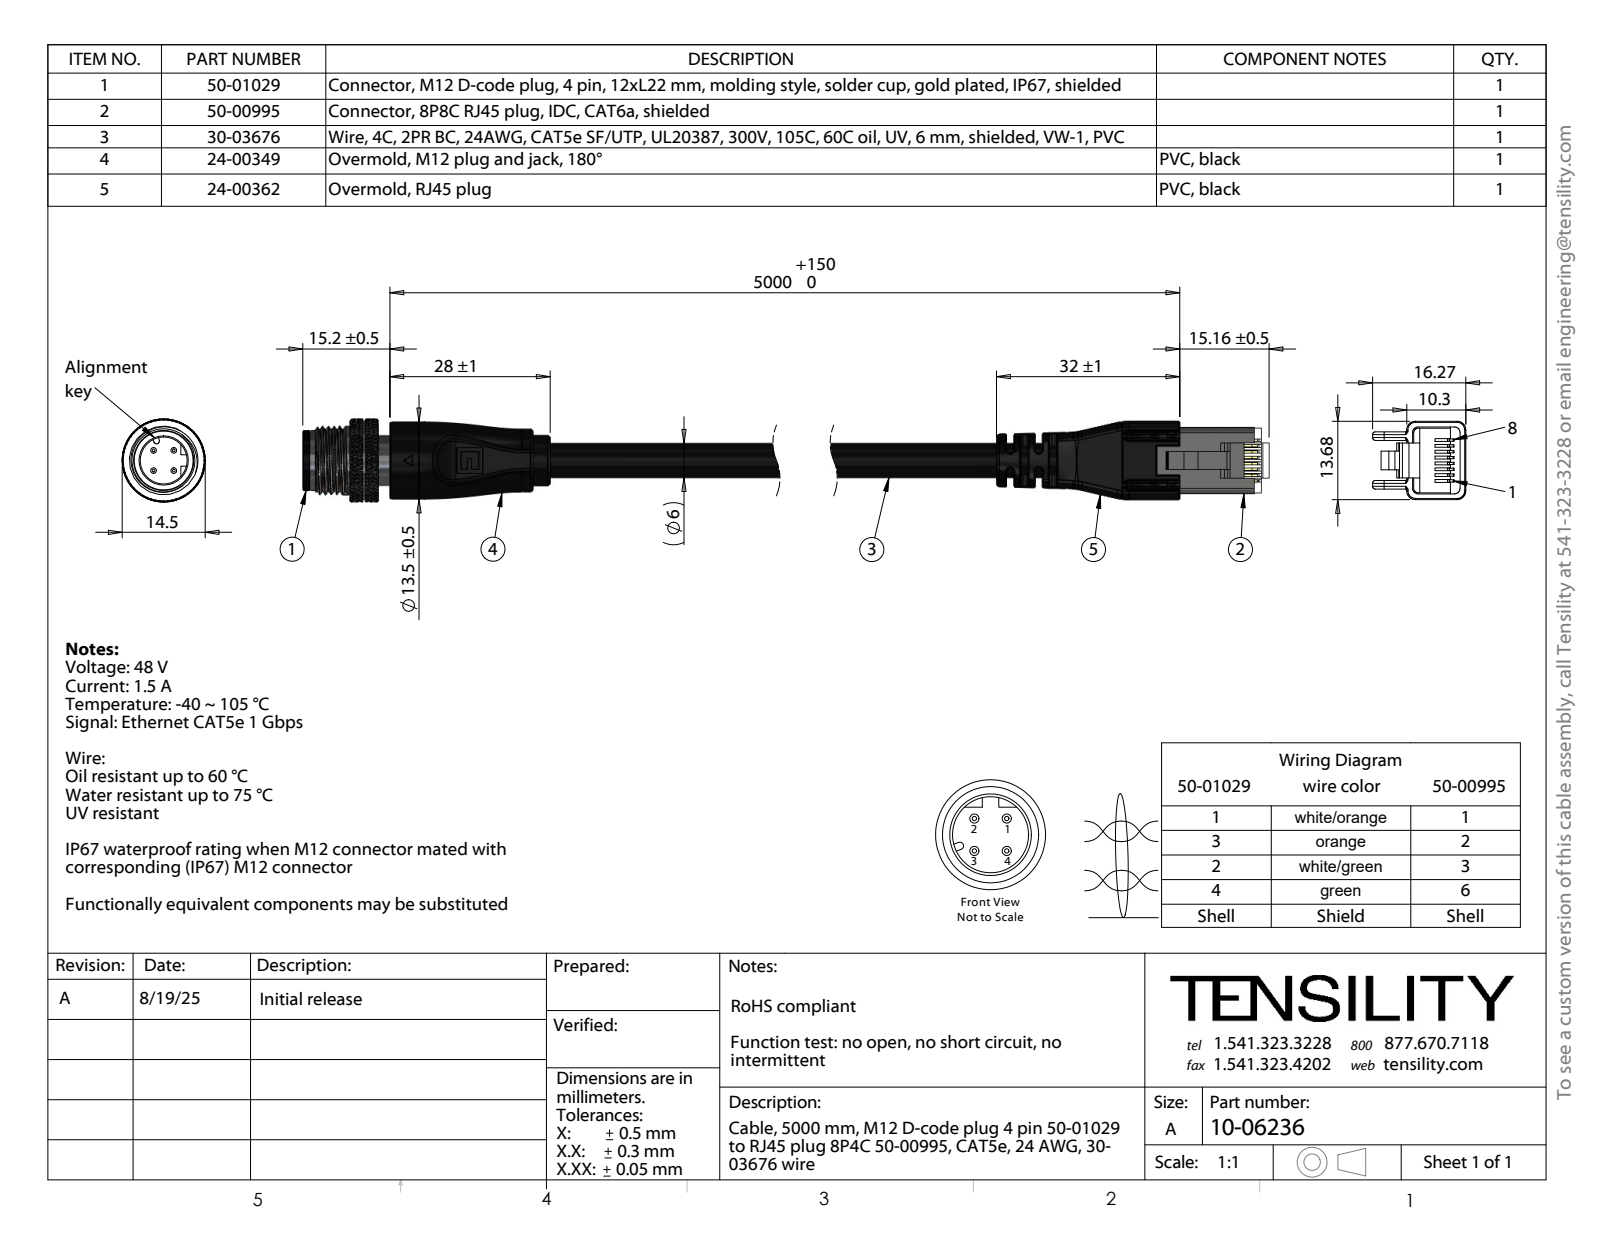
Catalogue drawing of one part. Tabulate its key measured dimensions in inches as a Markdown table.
| quantity | value |
| --- | --- |
| part name | 50-00995; 50-01029_默认; 24-00349_Mexico; 24-00362 (+6 more) |
| STEP written by | SolidWorks 2025 (CONFIG_CONTROL_DESIGN) |
| units | inches |
| bodies | 54 solids, 3209 faces (470 planar, 811 cylindrical, 1928 other) |
| overall size | 9.067 × 0.723 × 0.571 |
| volume | 0.849 in³ |
| surface area | 45.15 in² |
| round holes (diameter × count) | 0.008 × 28, 0.039 × 4, 0.041 × 4, 0.124 × 1, 0.126 × 1, 0.14 × 1, 0.315 × 1, 0.323 × 1, 0.346 × 1, 0.374 × 1 |
| round bosses / shafts (diameter × count) | 0.055 × 4, 0.571 × 1, 0.547 × 1, 0.531 × 1, 0.472 × 1, 0.433 × 1, 0.413 × 1, 0.366 × 1 |
| partial cylindrical surfaces (radius × count) | 0.008 × 11, 0.02 × 10, 0.059 × 10, 0.024 × 8, 0.039 × 5, 0.394 × 4, 0.031 × 2, 0.045 × 2 |
| main face-to-face distances | 0.049, 0.098, 0.039, 0.148, 0.197, 0.366, 0.276, 7.854, 0.499, 0.46 |
| hole center spacings | 0.042, 0.075, 0.082, 0.014, 0.043, 0.067, 0.071, 0.089 |
